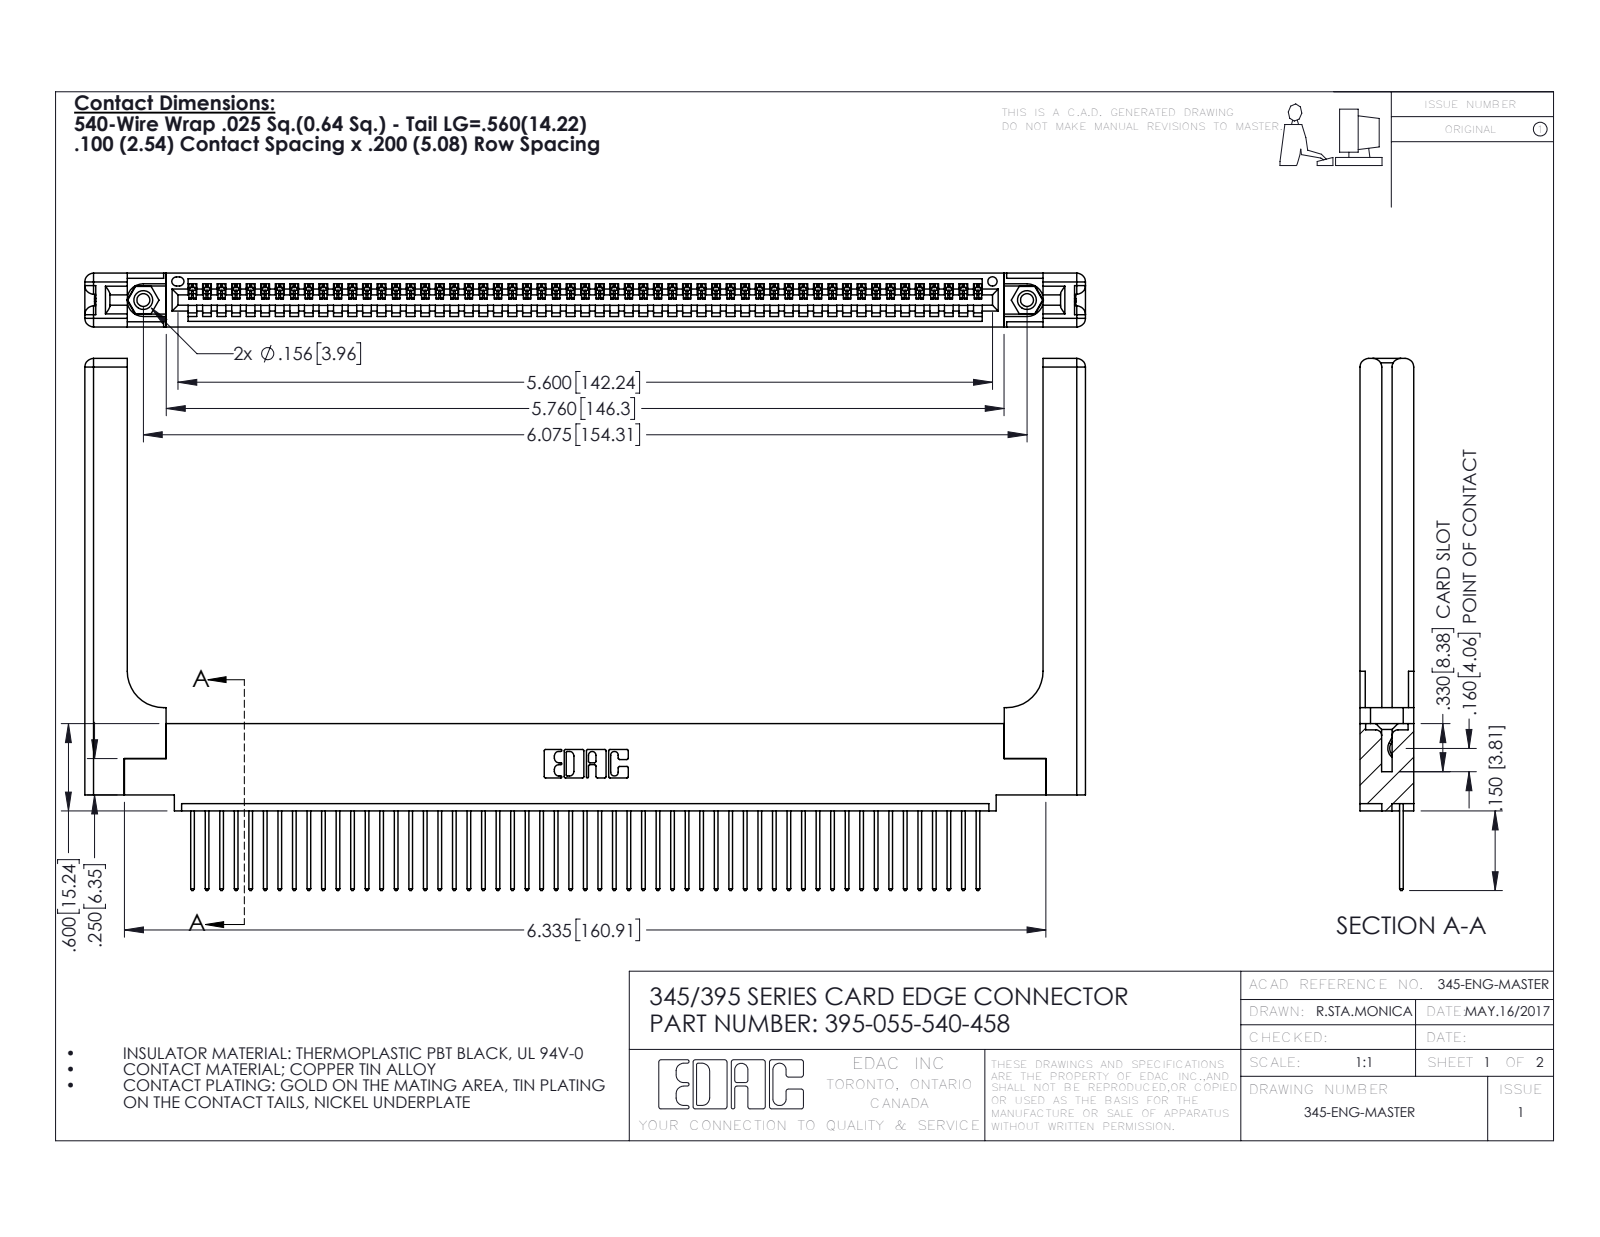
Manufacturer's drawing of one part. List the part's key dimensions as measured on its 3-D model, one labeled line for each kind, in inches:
Part name (STEP PRODUCT): 345-292-001_345-293-140; 395-055-540-458; 345-220-058_345-220-058; 345-250-001_345-250-001-102 (+1 more)
STEP written by: SolidWorks 2016 (CONFIG_CONTROL_DESIGN)
Units: inches
Bodies: 60 solids, 3576 faces (2432 planar, 1084 cylindrical, 60 other)
Overall size (bounding box): 6.879 × 3.657 × 0.37
Volume: 1.538 in³ · Surface area: 43.86 in²
Round holes (diameter × count): ⌀0.089 ×2, ⌀0.125 ×2, ⌀0.156 ×2, ⌀0.064 ×1
Round bosses / shafts (diameter × count): ⌀0.155 ×2
Partial cylindrical surfaces — rounded edges, fillets, slot ends (radius × count): R0.006 ×110, R0.01 ×110, R0.01 ×22, R0.06 ×16, R0.007 ×6, R0.031 ×6, R0.026 ×3, R0.03 ×2
Main face-to-face distances: 0.072, 0.298, 0.37, 0.098, 0.272, 0.025, 0.2, 0.225, 0.148, 0.15
Hole centre spacings: 0.27, 5.839, 6.075
